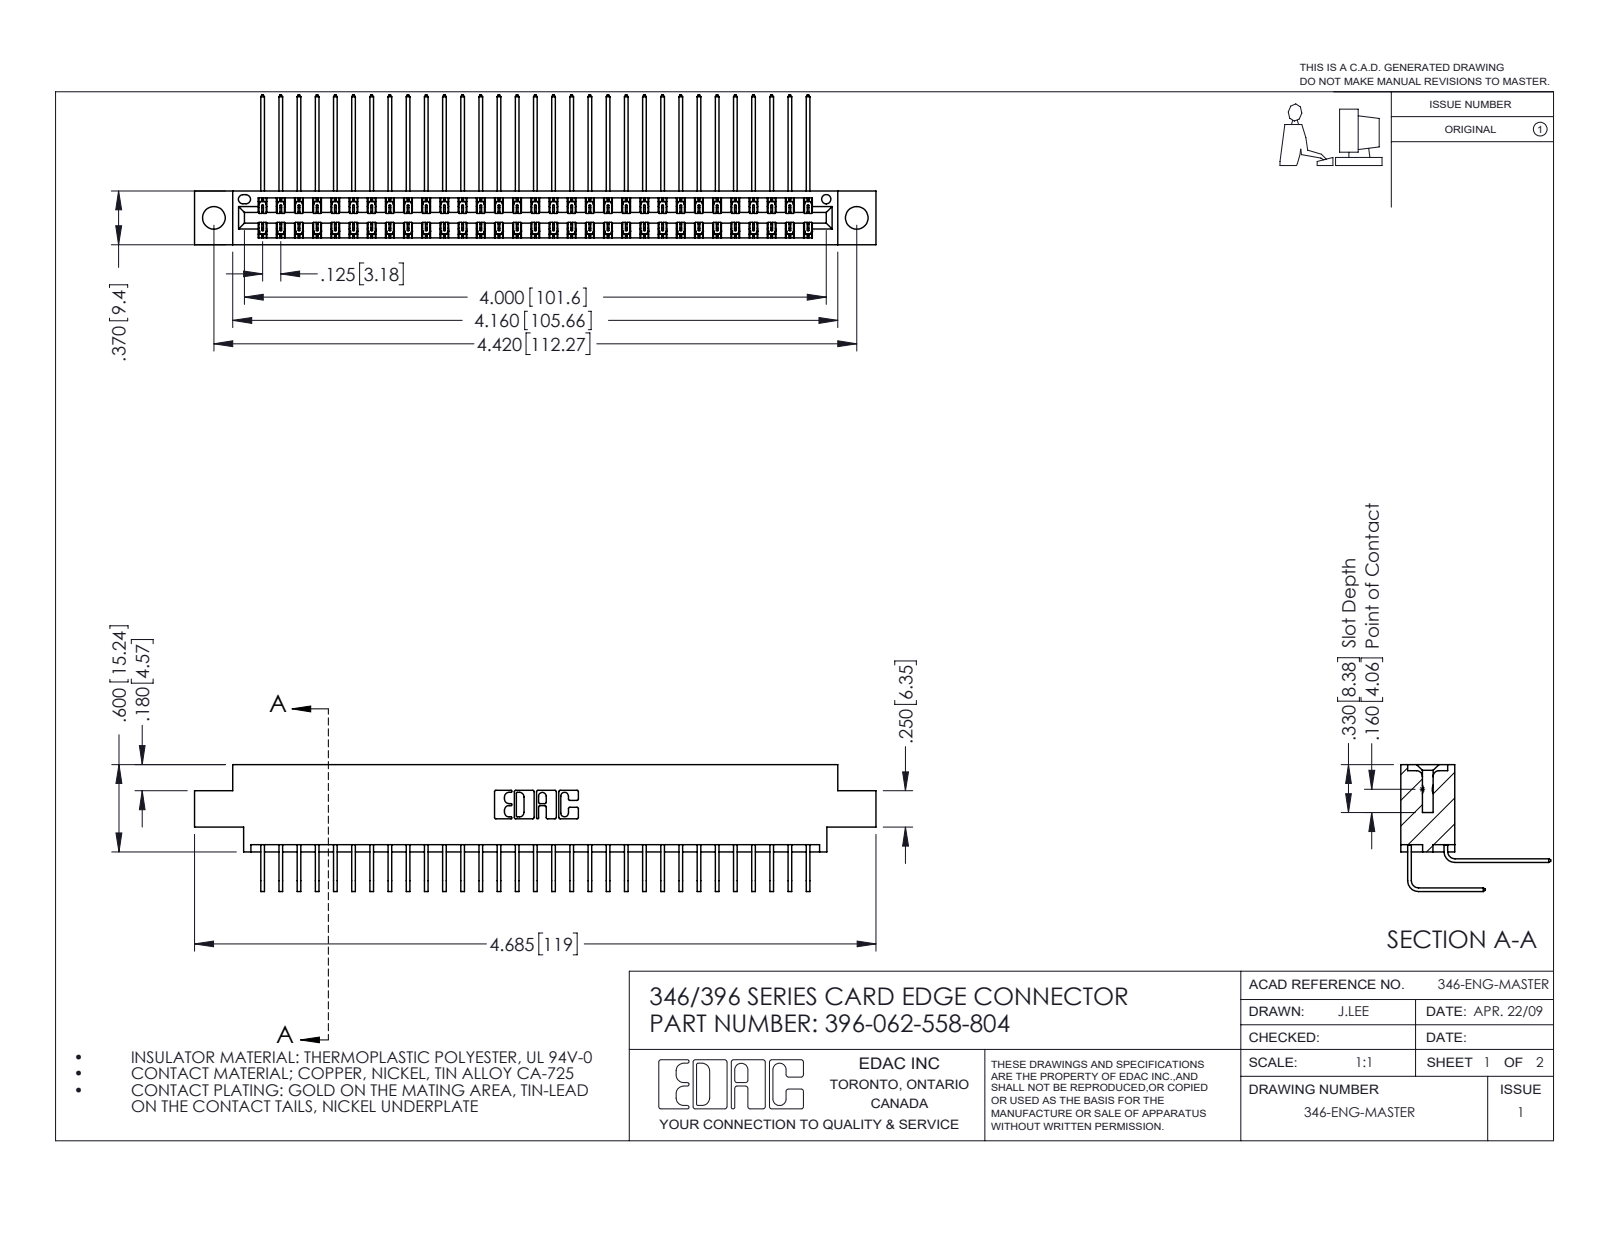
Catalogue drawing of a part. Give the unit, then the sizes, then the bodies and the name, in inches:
Units: inches
Overall size (bounding box): 4.685 × 1.03 × 0.873
Round holes (diameter × count): ⌀0.156 ×2, ⌀0.064 ×1
Partial cylindrical surfaces — rounded edges, fillets, slot ends (radius × count): R0.006 ×93, R0.01 ×22, R0.007 ×6, R0.031 ×6, R0.026 ×3, R0.014 ×2, R0.022 ×2, R0.024 ×2
Main face-to-face distances: 0.322, 0.048, 0.025, 0.37, 0.25, 0.298, 0.072, 0.275, 0.148, 0.222
Hole centre spacings: 0.246, 4.212, 4.42
Volume: 0.71 in³ · Surface area: 27.17 in²
Bodies: 63 solids, 3474 faces (2374 planar, 1100 cylindrical, 0 other)
Part name (STEP PRODUCT): 396-062-558-804; 346 Part_0.170 Offset - 0.156 Dia-TH; 345-292-001_558 559 Tail - 1; 345-292-001_558 Tail - 2
STEP written by: SolidWorks 2016 (CONFIG_CONTROL_DESIGN)
